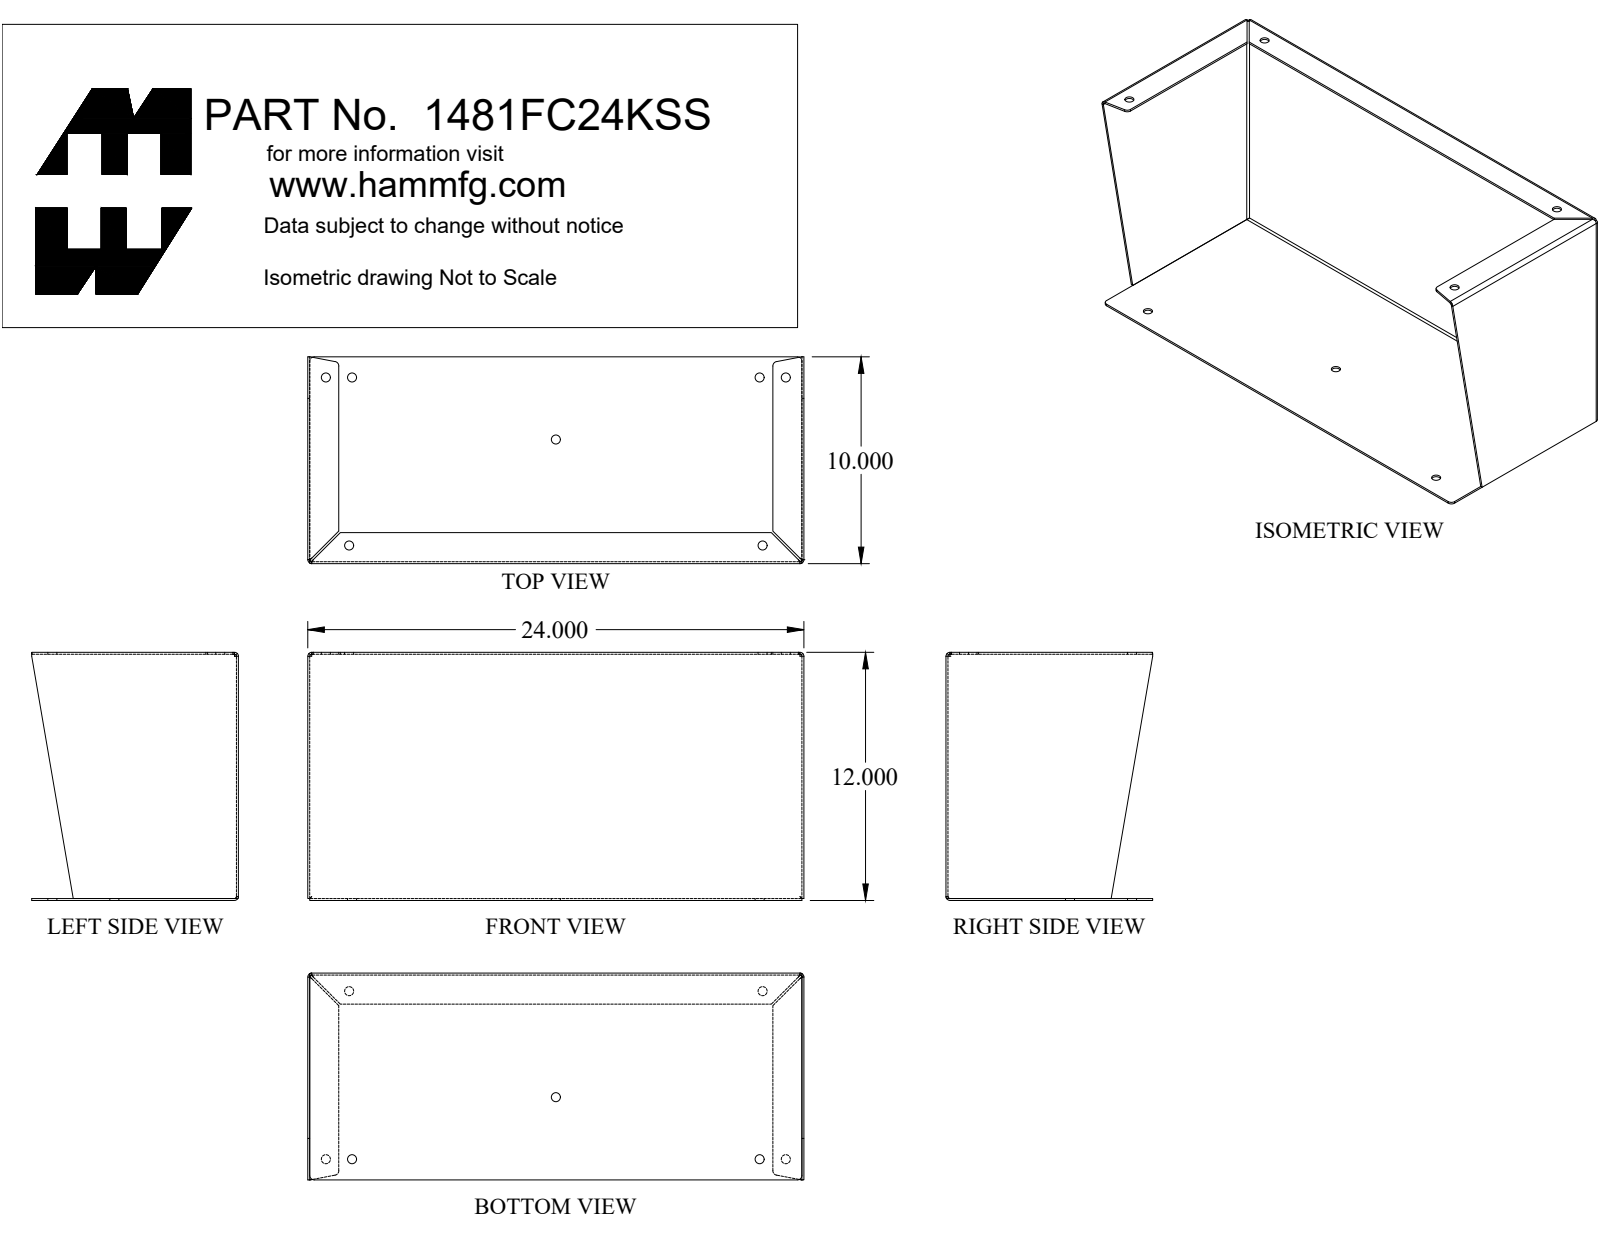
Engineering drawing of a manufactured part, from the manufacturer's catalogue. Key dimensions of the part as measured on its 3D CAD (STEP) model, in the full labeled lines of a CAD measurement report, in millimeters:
Part name (STEP PRODUCT): 1481FC24KSS
STEP written by: SolidWorks 2019 (CONFIG_CONTROL_DESIGN)
Units: millimetres
Bodies: 1 solid, 71 faces (42 planar, 23 cylindrical, 6 other)
Overall size (bounding box): 609.6 × 304.8 × 254
Volume: 1 223 000 mm³ · Surface area: 1 023 000 mm²
Round holes (diameter × count): ⌀11.1 ×7
Partial cylindrical surfaces — rounded edges, fillets, slot ends (radius × count): R2.4 ×6, R4.8 ×6, R5.6 ×4
Main face-to-face distances: 2.4, 2.4, 607.2, 609.6, 604.8, 300, 302.4, 302.4, 304.8, 35.7
Hole centre spacings: 206.4, 208.3, 261.8, 285.4, 545, 32.2, 32.2, 292.7
